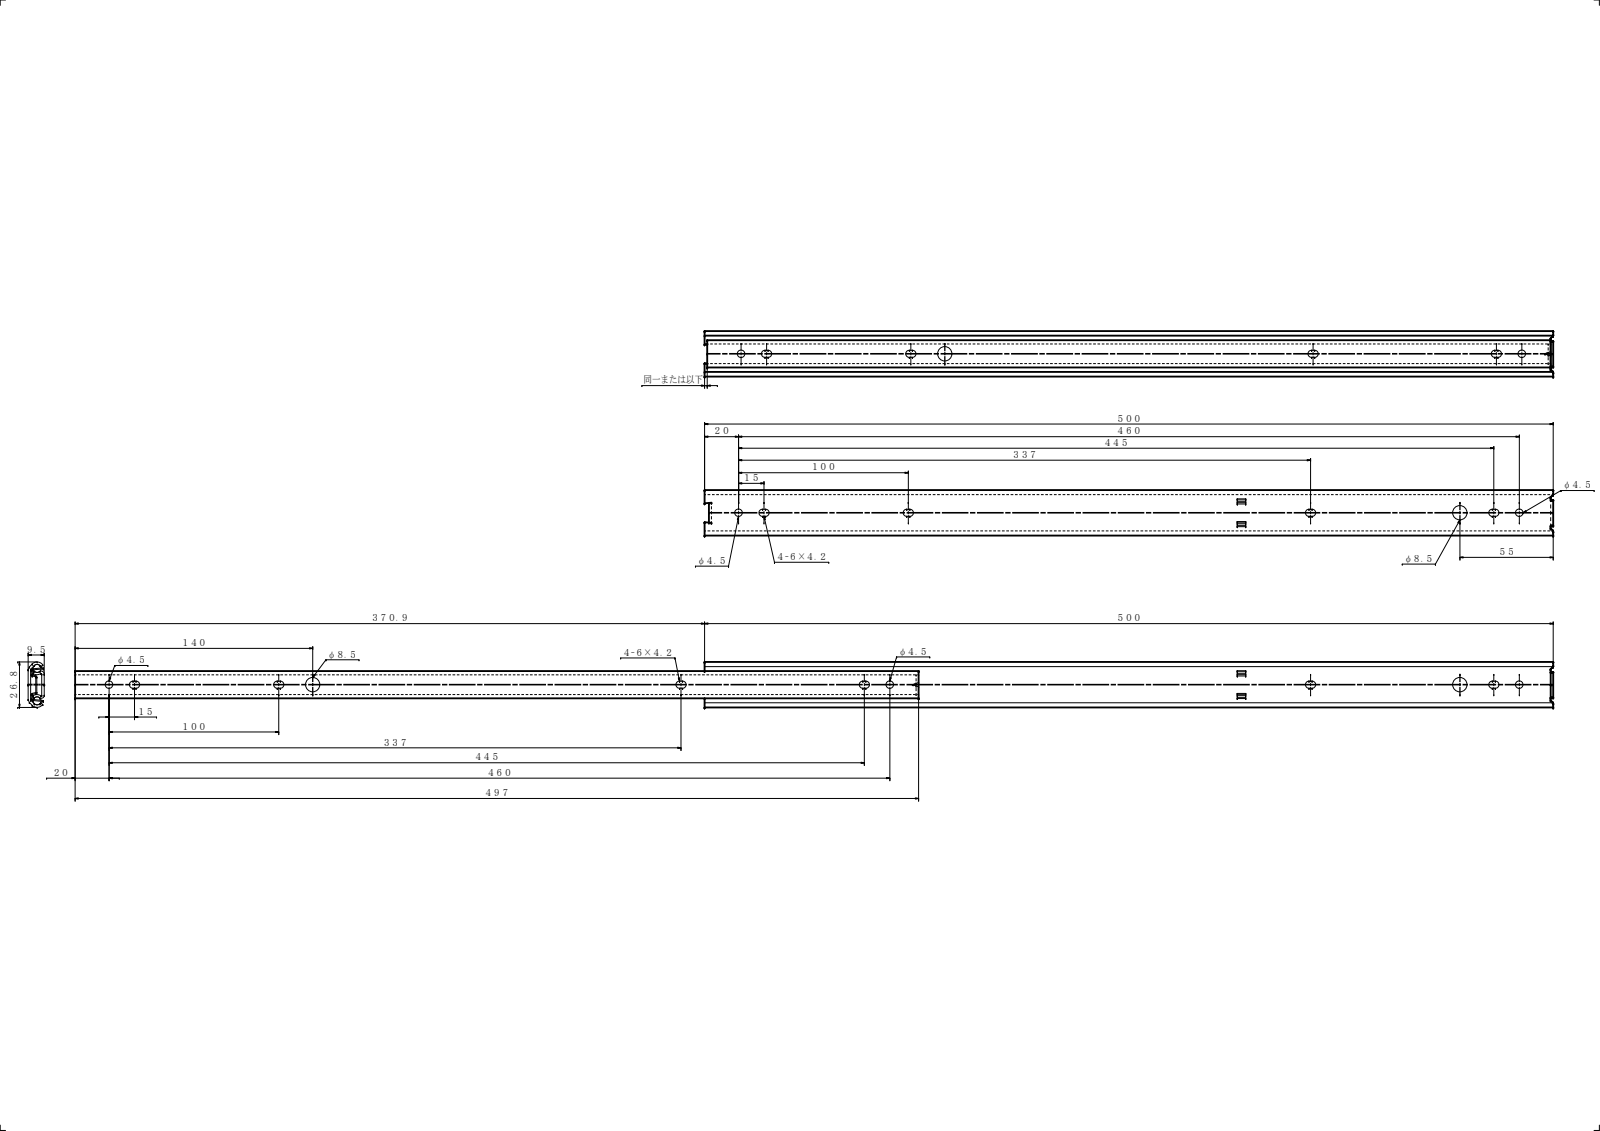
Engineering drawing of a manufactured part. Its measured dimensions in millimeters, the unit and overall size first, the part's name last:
Units: millimetres
Overall size (bounding box): 870.9 × 26.8 × 9.5
Round holes (diameter × count): ⌀4.5 ×4, ⌀8.5 ×2
Partial cylindrical surfaces — rounded edges, fillets, slot ends (radius × count): R2.1 ×16, R2 ×10, R1 ×5, R0.5 ×4, R0.18 ×2, R1.3 ×2, R1.68 ×2, R2.38 ×2
Main face-to-face distances: 1.5, 8, 9.5, 6.5, 373.9, 372.4, 496.02, 122.12, 375.4, 497.52
Hole centre spacings: 370.9, 460, 35, 89.1, 120, 250.9, 335.9, 340
Volume: 46 066 mm³ · Surface area: 65 342 mm²
Bodies: 2 solids, 134 faces (61 planar, 73 cylindrical, 0 other)
Part name (STEP PRODUCT): U2721-500 IM; U2721_500; U2721-500 OM
STEP written by: SolidWorks 2019 (CONFIG_CONTROL_DESIGN)
